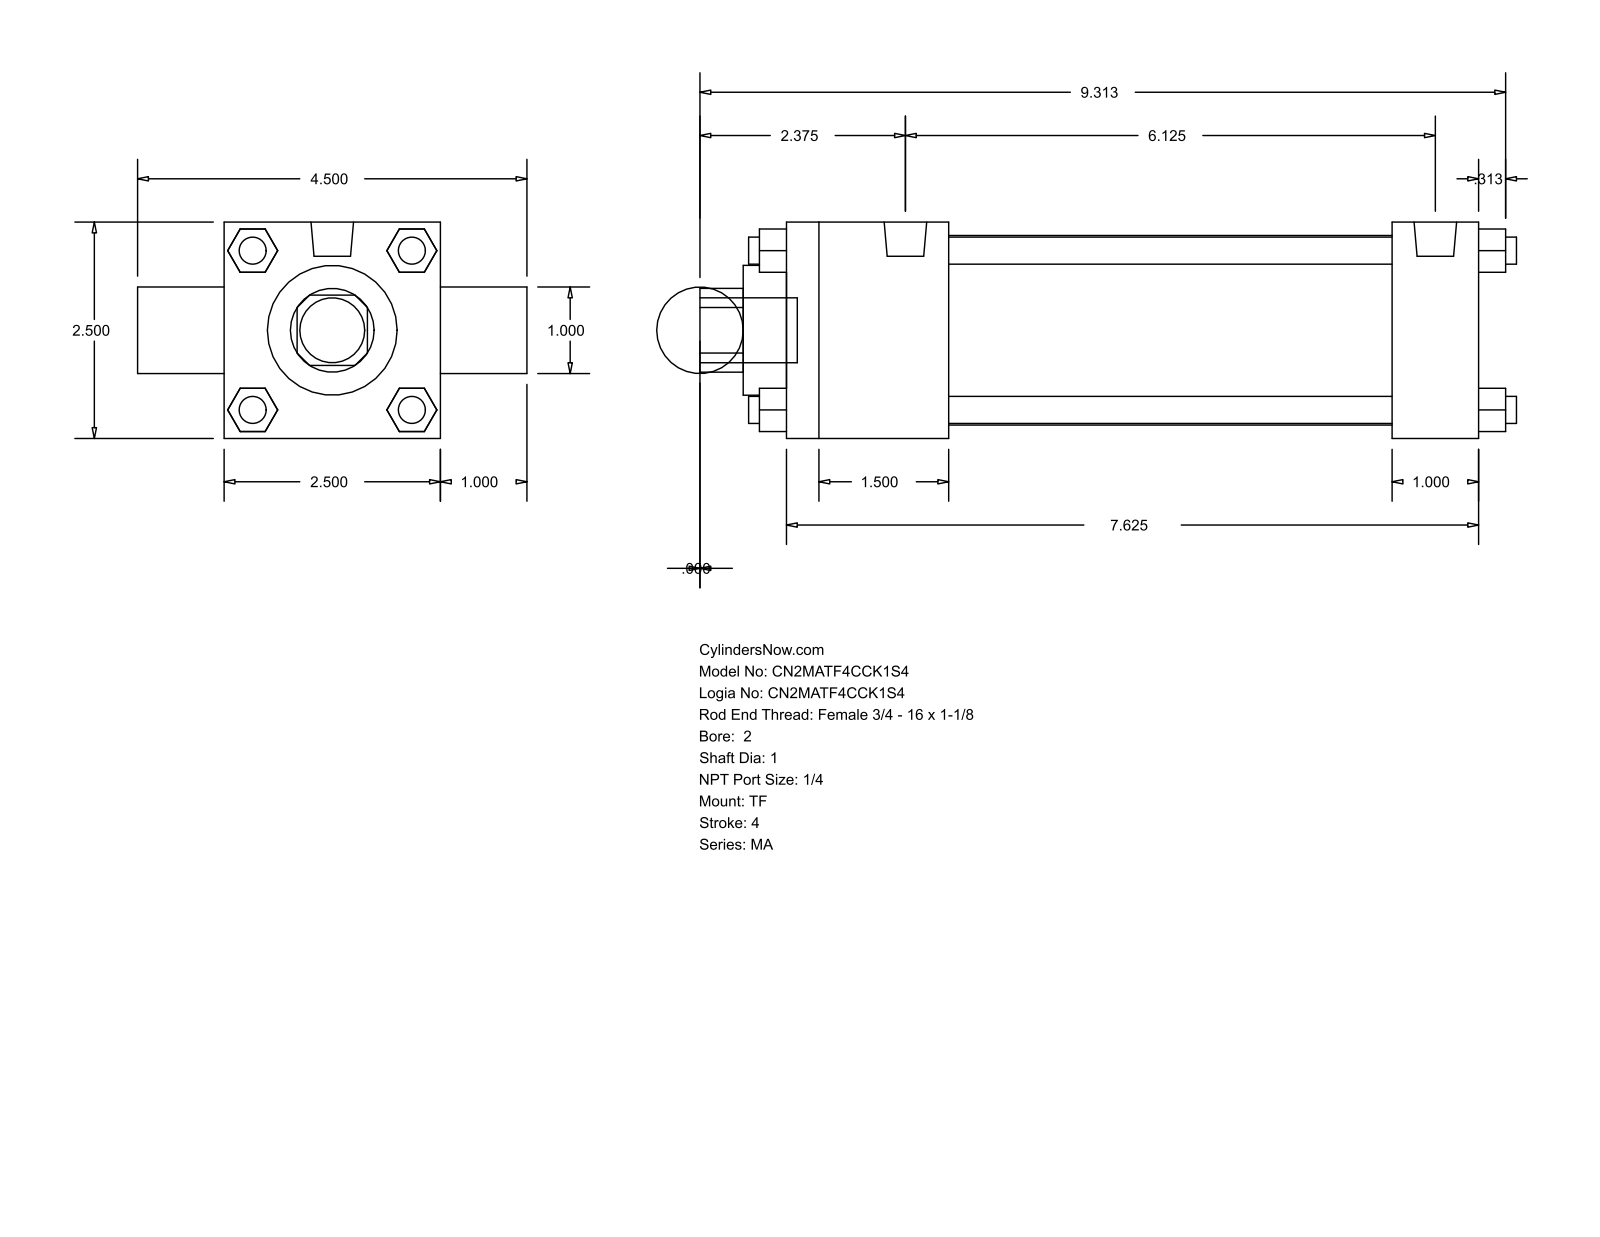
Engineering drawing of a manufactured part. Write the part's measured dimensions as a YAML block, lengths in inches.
part_name: "MA_TF__0200_1"
step_written_by: "GSSL Pune (CONFIG_CONTROL_DESIGN)"
units: inches
bodies: {solids: 0, faces: 120, planar: 92, cylindrical: 28, other: 0}
overall_size: [9.437, 4.5, 2.5]
round_holes:
  - {diameter: 1, count: 2}
  - {diameter: 1.5, count: 1}
  - {diameter: 2.19, count: 1}
round_bosses_or_shafts:
  - {diameter: 0.313, count: 7}
  - {diameter: 0.492, count: 2}
  - {diameter: 0.75, count: 1}
partial_cylinders:
  - {radius: 0.484, count: 1}
face_to_face_distances: [2.5, 1, 8, 0.5, 1.875, 7, 5.125, 6.125, 3.5, 1.593]
